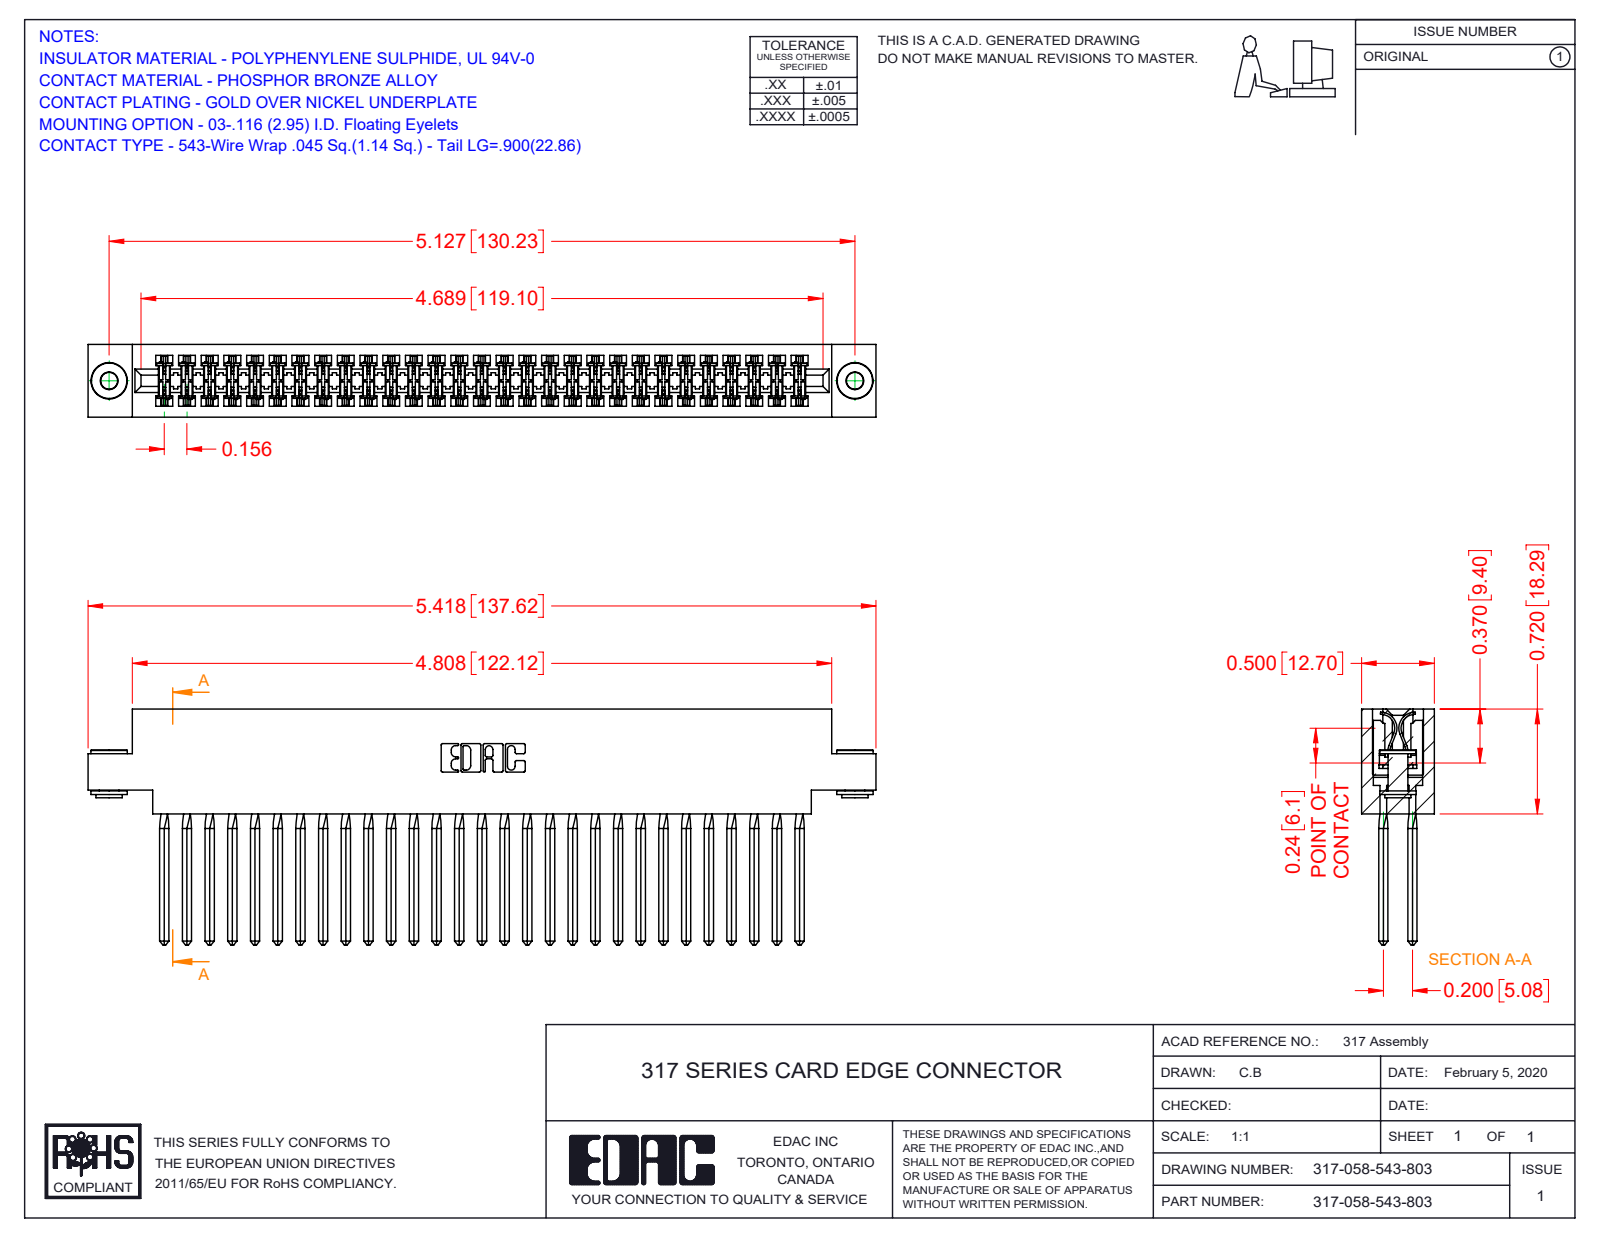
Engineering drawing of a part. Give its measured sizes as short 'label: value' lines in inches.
name: 317 Part_.156 Dia - TH; 317-290-001_543; 317-058-543-803; 345-250-002_345-250-002-102
written by: SolidWorks 2016 (CONFIG_CONTROL_DESIGN)
unit: in
bodies: 61 solids, 5302 faces (4302 planar, 760 cylindrical, 240 other)
size: 5.418 × 1.62 × 0.5
volume: 1.401 in³; area: 53.54 in²
holes: 2× ⌀0.116, 2× ⌀0.156
bosses: 2× ⌀0.25, 2× ⌀0.18, 2× ⌀0.136
rounds: 116× R0.015, 22× R0.01, 6× R0.007, 6× R0.031, 3× R0.026, 2× R0.095, 2× R0.1, 2× R0.11
face distances: 0.5, 0.075, 0.425, 0.35, 0.11, 0.195, 0.094, 0.2, 0.72, 0.115
hole spacings: 5.127
